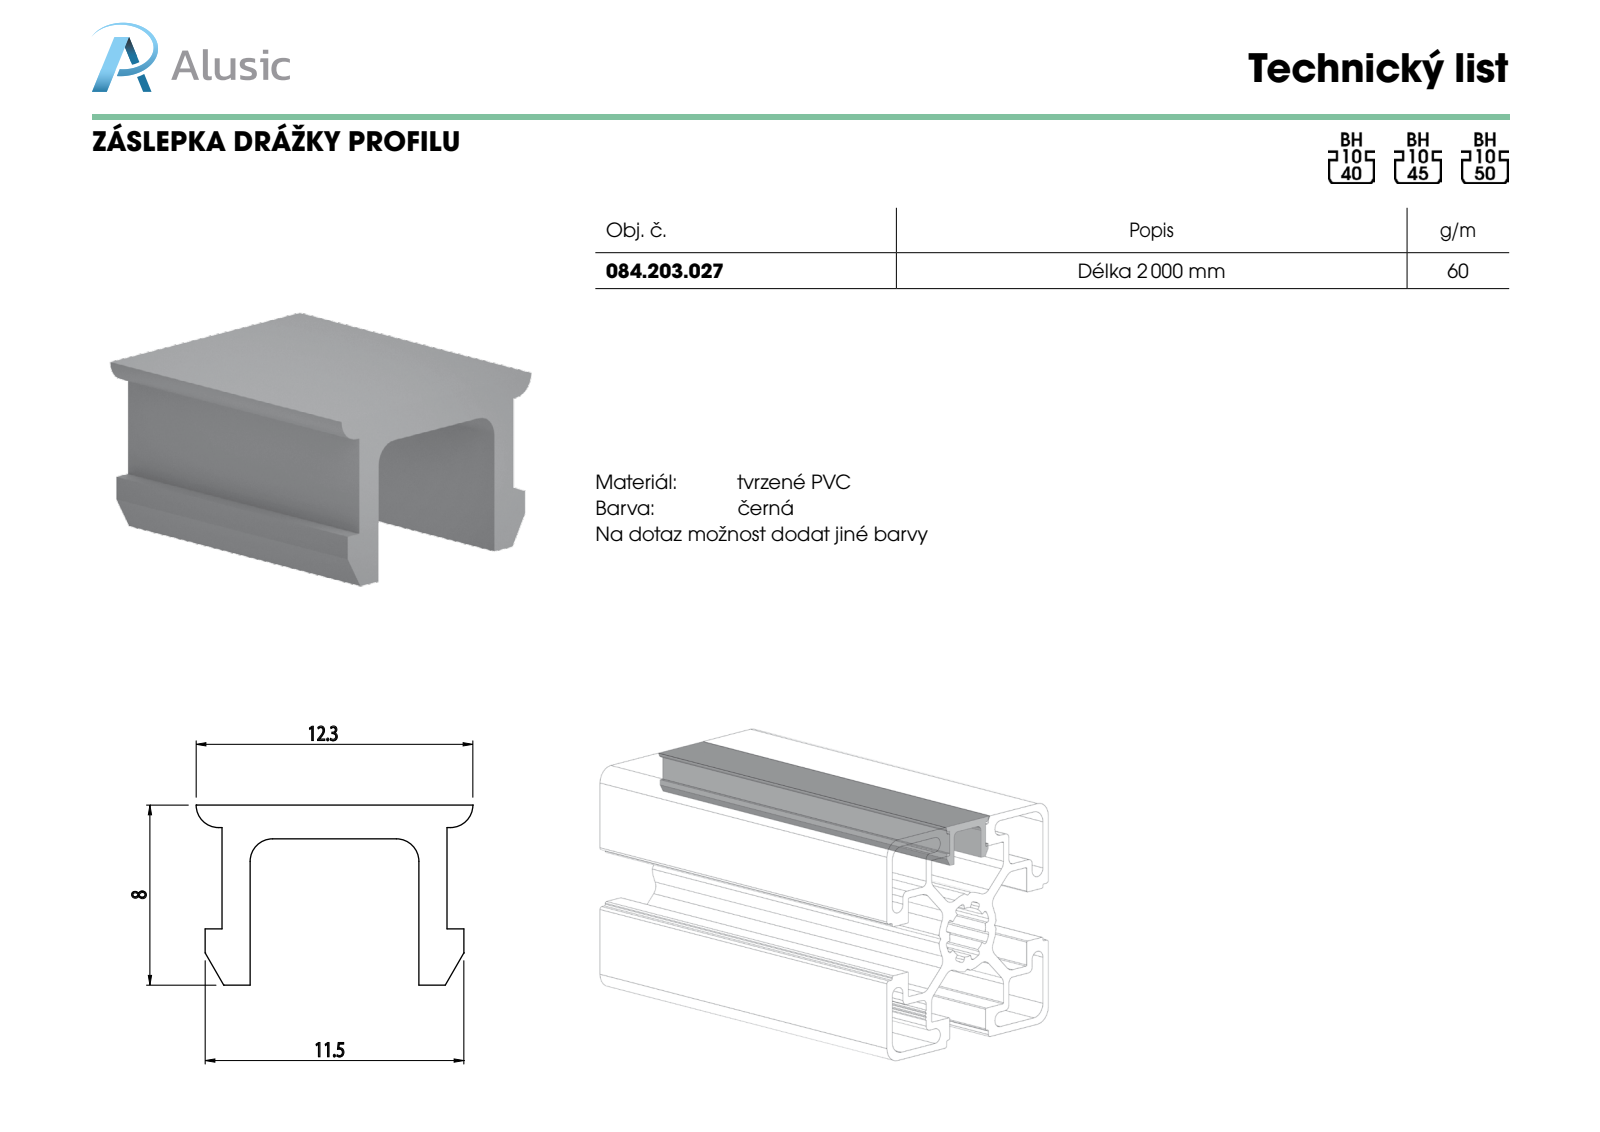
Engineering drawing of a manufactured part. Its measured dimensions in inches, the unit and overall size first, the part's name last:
Units: inches
Overall size (bounding box): 3.937 × 0.484 × 0.315
Partial cylindrical surfaces — rounded edges, fillets, slot ends (radius × count): R0.039 ×4
Main face-to-face distances: 0.049, 0.344, 0.295, 0.059, 0.394, 0.256, 0.315, 0.03, 0.079, 0.374
Volume: 0.22 in³ · Surface area: 8.43 in²
Bodies: 1 solid, 22 faces (18 planar, 4 cylindrical, 0 other)
Part name (STEP PRODUCT): 084.203.027
STEP written by: SolidWorks 2016 (CONFIG_CONTROL_DESIGN)
